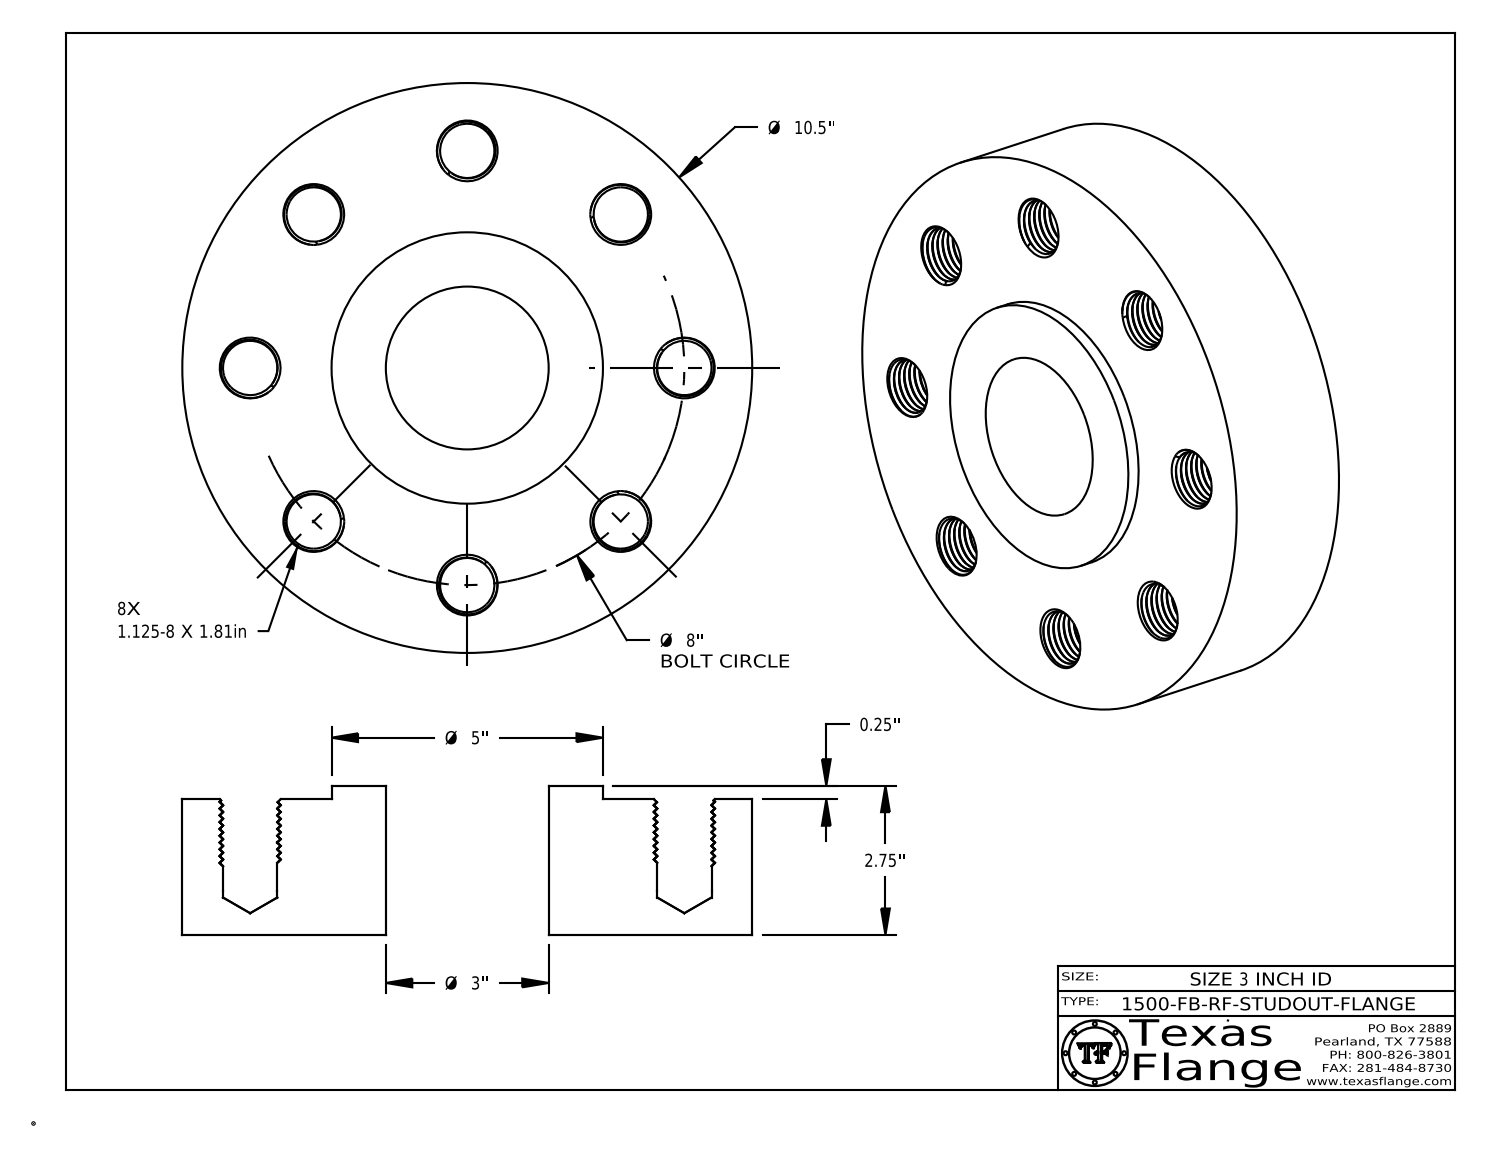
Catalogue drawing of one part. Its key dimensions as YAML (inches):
part_name: "3-1500-FB-RF-STUDOUT-FLANGE"
step_written_by: "CATIA V5 STEP AP214 (AUTOMOTIVE_DESIGN)"
units: inches
bodies: {solids: 1, faces: 938, planar: 368, cylindrical: 202, other: 368}
overall_size: [10.5, 10.5, 2.75]
volume: 189
surface_area: 331.7
round_holes:
  - {diameter: 1, count: 8}
  - {diameter: 3, count: 1}
round_bosses_or_shafts:
  - {diameter: 0.061, count: 8}
  - {diameter: 10.5, count: 1}
  - {diameter: 5, count: 1}
  - {diameter: 0.788, count: 1}
face_to_face_distances: [2.5, 0.25, 2.75, 2.735, 2.485, 0.015, 0.298, 0.293, 0.054, 0.248]
hole_center_spacings: [3.061, 4, 5.657, 7.391, 8, 8]
